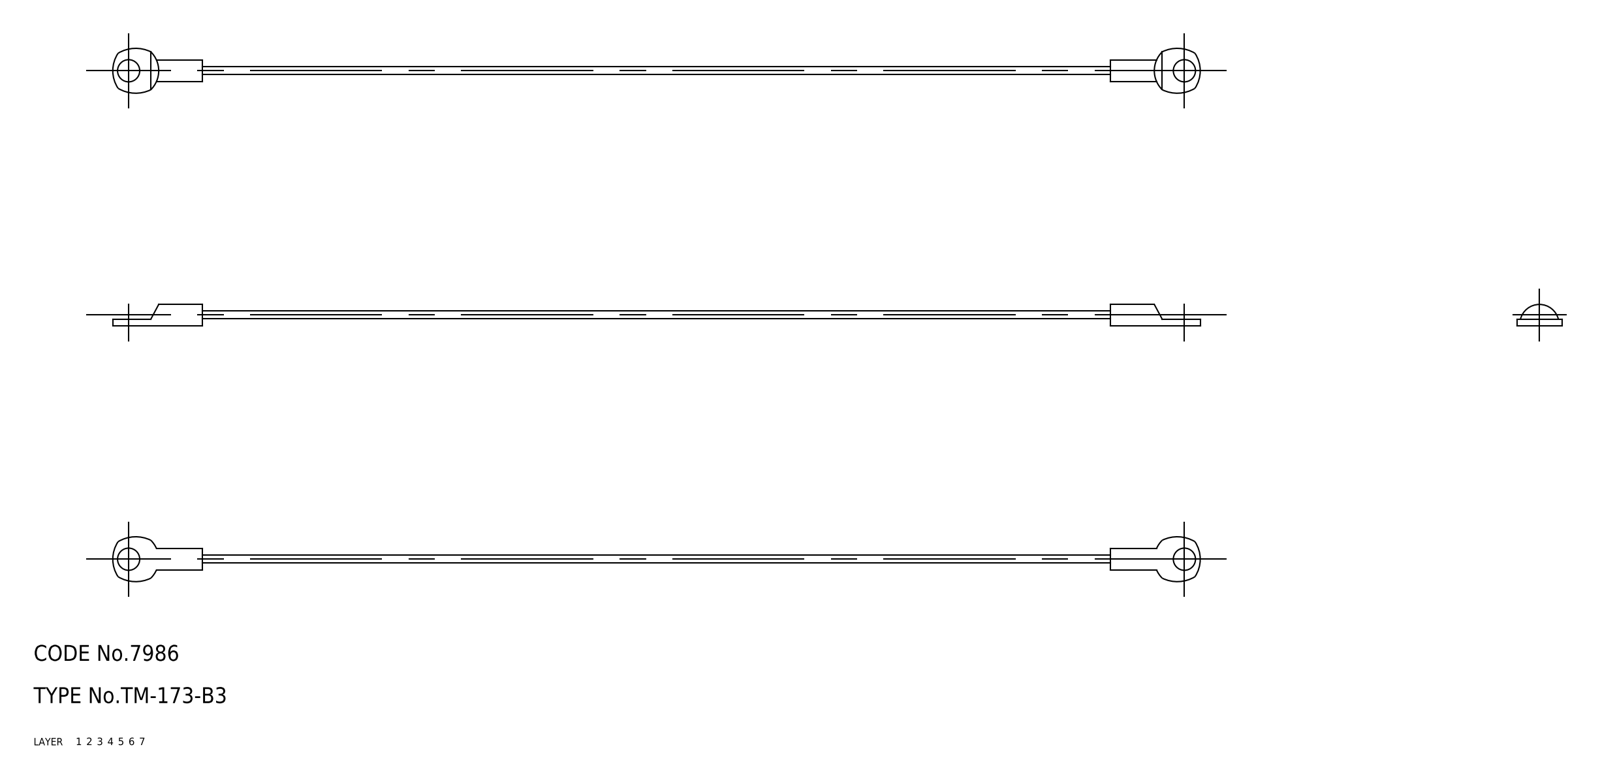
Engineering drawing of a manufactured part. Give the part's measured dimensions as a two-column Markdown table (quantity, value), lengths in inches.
| quantity | value |
| --- | --- |
| part name | terminal; wire; TM_173_B3_28420_36 |
| STEP written by | CADfix (AUTOMOTIVE_DESIGN) |
| units | inches |
| bodies | 3 solids, 56 faces (0 planar, 0 cylindrical, 56 other) |
| overall size | 8.11 × 0.335 × 0.157 |
| volume | 0.039 in³ |
| surface area | 2.297 in² |
